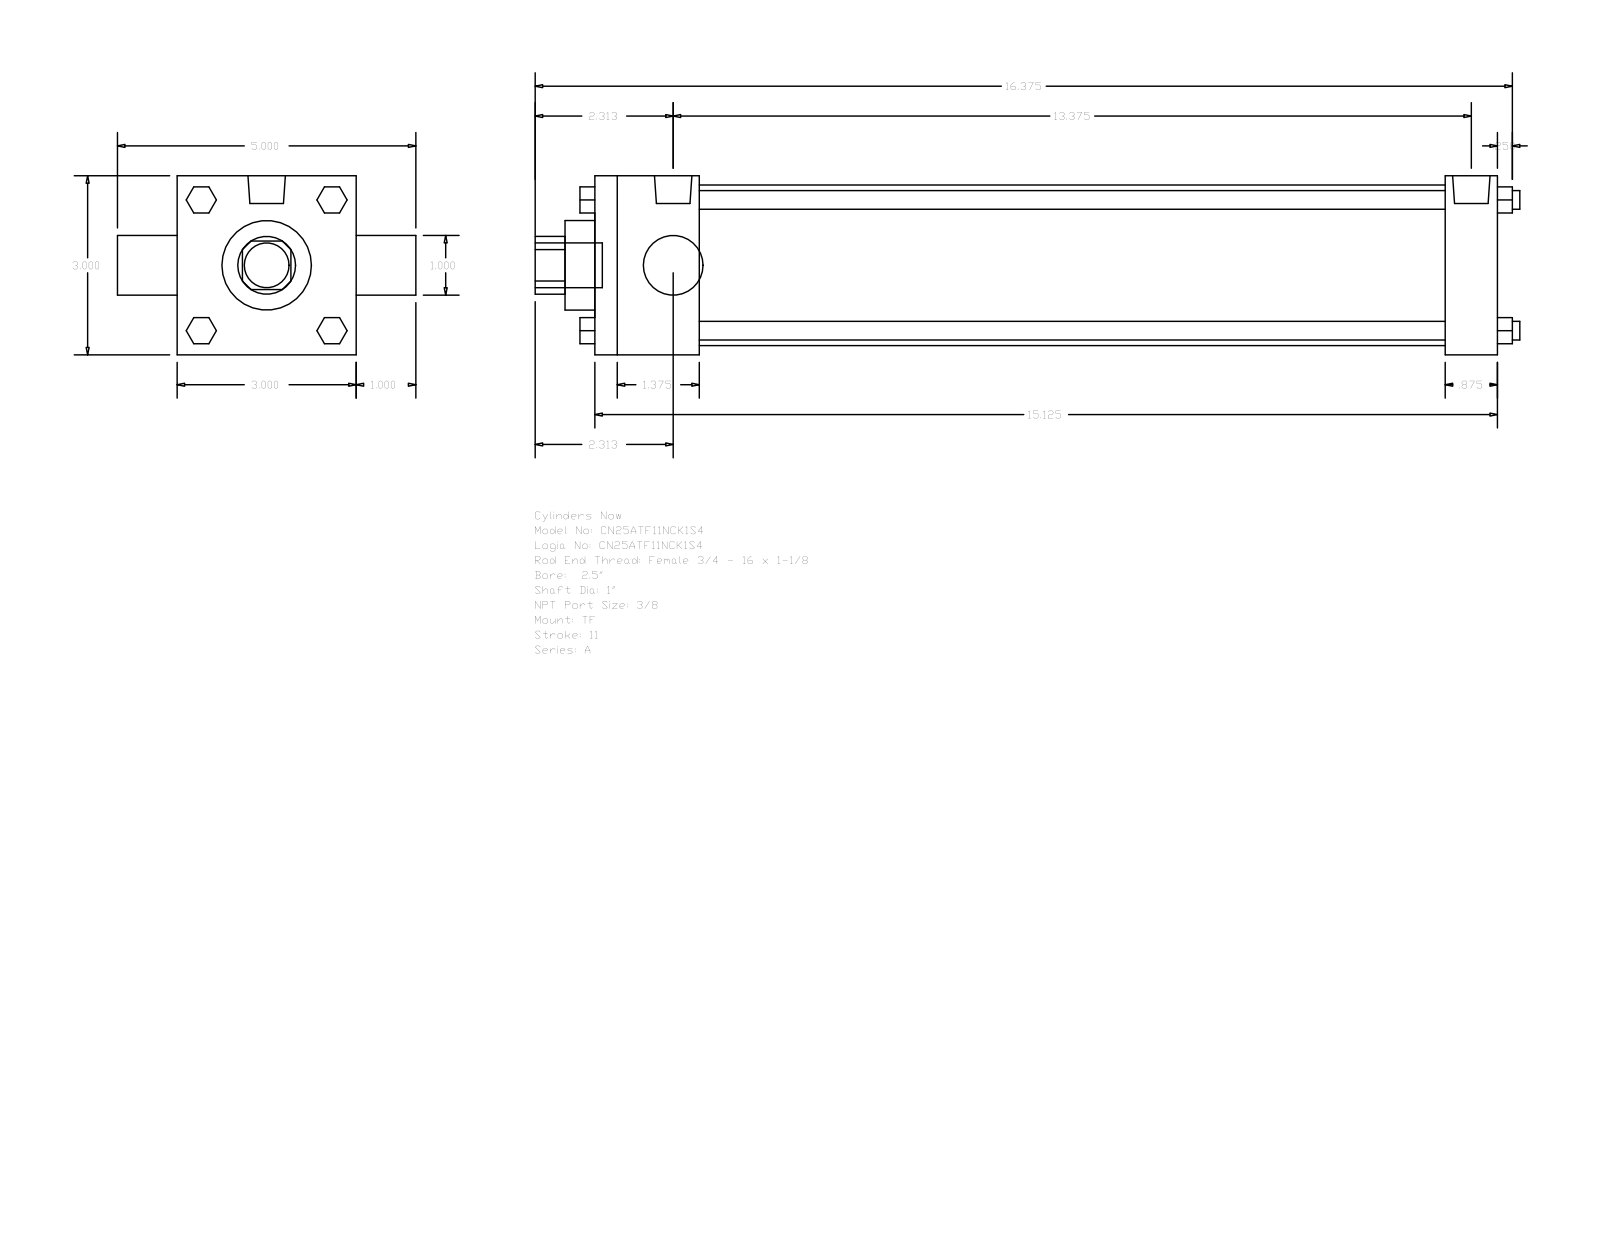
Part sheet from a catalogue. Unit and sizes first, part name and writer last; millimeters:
Units: millimetres
Overall size (bounding box): 419.1 × 127 × 76.2
Round holes (diameter × count): ⌀25.4 ×2, ⌀38.1 ×1, ⌀68.33 ×1
Round bosses / shafts (diameter × count): ⌀7.94 ×4, ⌀5.56 ×3, ⌀15.93 ×2, ⌀19.05 ×1
Partial cylindrical surfaces — rounded edges, fillets, slot ends (radius × count): R12.29 ×1
Main face-to-face distances: 76.2, 384.17, 44.45, 361.95, 317.5, 339.72, 22.22, 25.4, 101.6, 12.7
Bodies: 0 solids, 120 faces (92 planar, 28 cylindrical, 0 other)
Part name (STEP PRODUCT): A_TF__0250_1
STEP written by: GSSL Pune (CONFIG_CONTROL_DESIGN)
